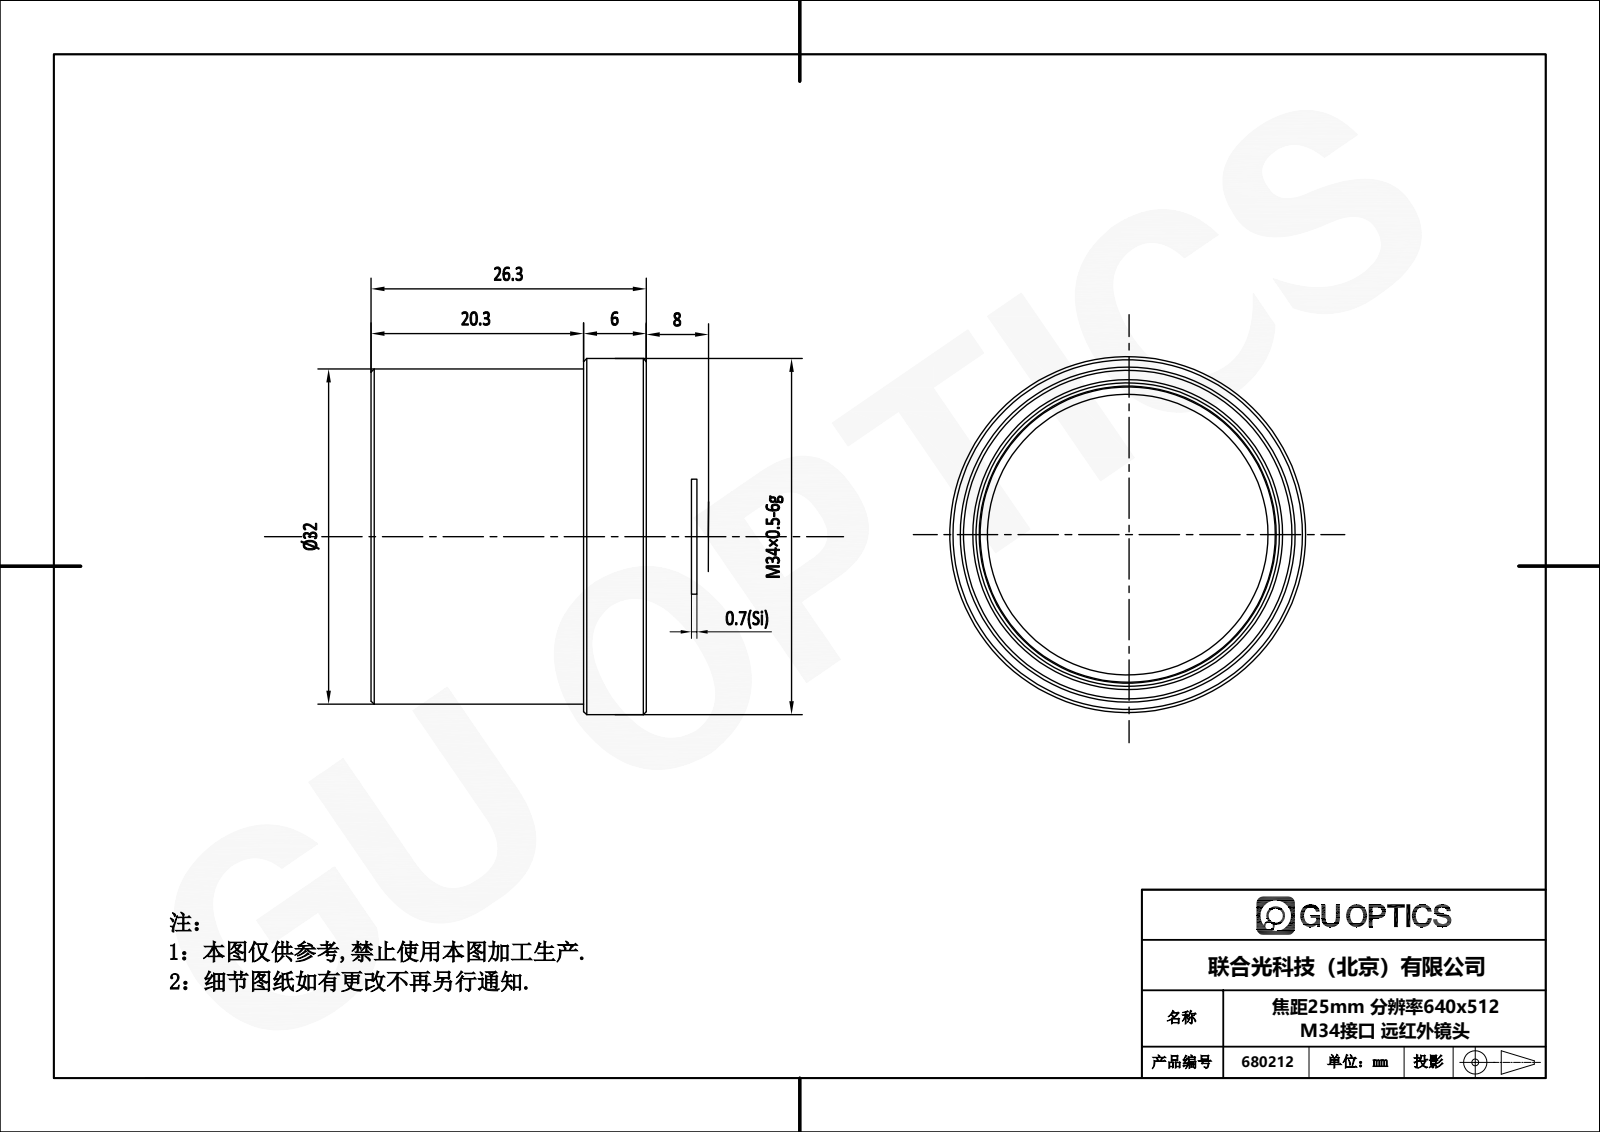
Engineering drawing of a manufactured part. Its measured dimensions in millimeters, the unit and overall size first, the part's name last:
Units: millimetres
Overall size (bounding box): 34 × 34 × 26.3
Round holes (diameter × count): ⌀18 ×1, ⌀28.4 ×1, ⌀29 ×1, ⌀29.2 ×1, ⌀29.8 ×1
Round bosses / shafts (diameter × count): ⌀32 ×1, ⌀26.8 ×1
Main face-to-face distances: 26.3, 20.3, 6, 5.9, 14.4, 20.4, 2, 3.9, 18.3, 24.3
Volume: 18 644 mm³ · Surface area: 5 308 mm²
Bodies: 1 solid, 24 faces (7 planar, 7 cylindrical, 10 other)
Part name (STEP PRODUCT): 25mm
STEP written by: SolidWorks 2020 (CONFIG_CONTROL_DESIGN)
